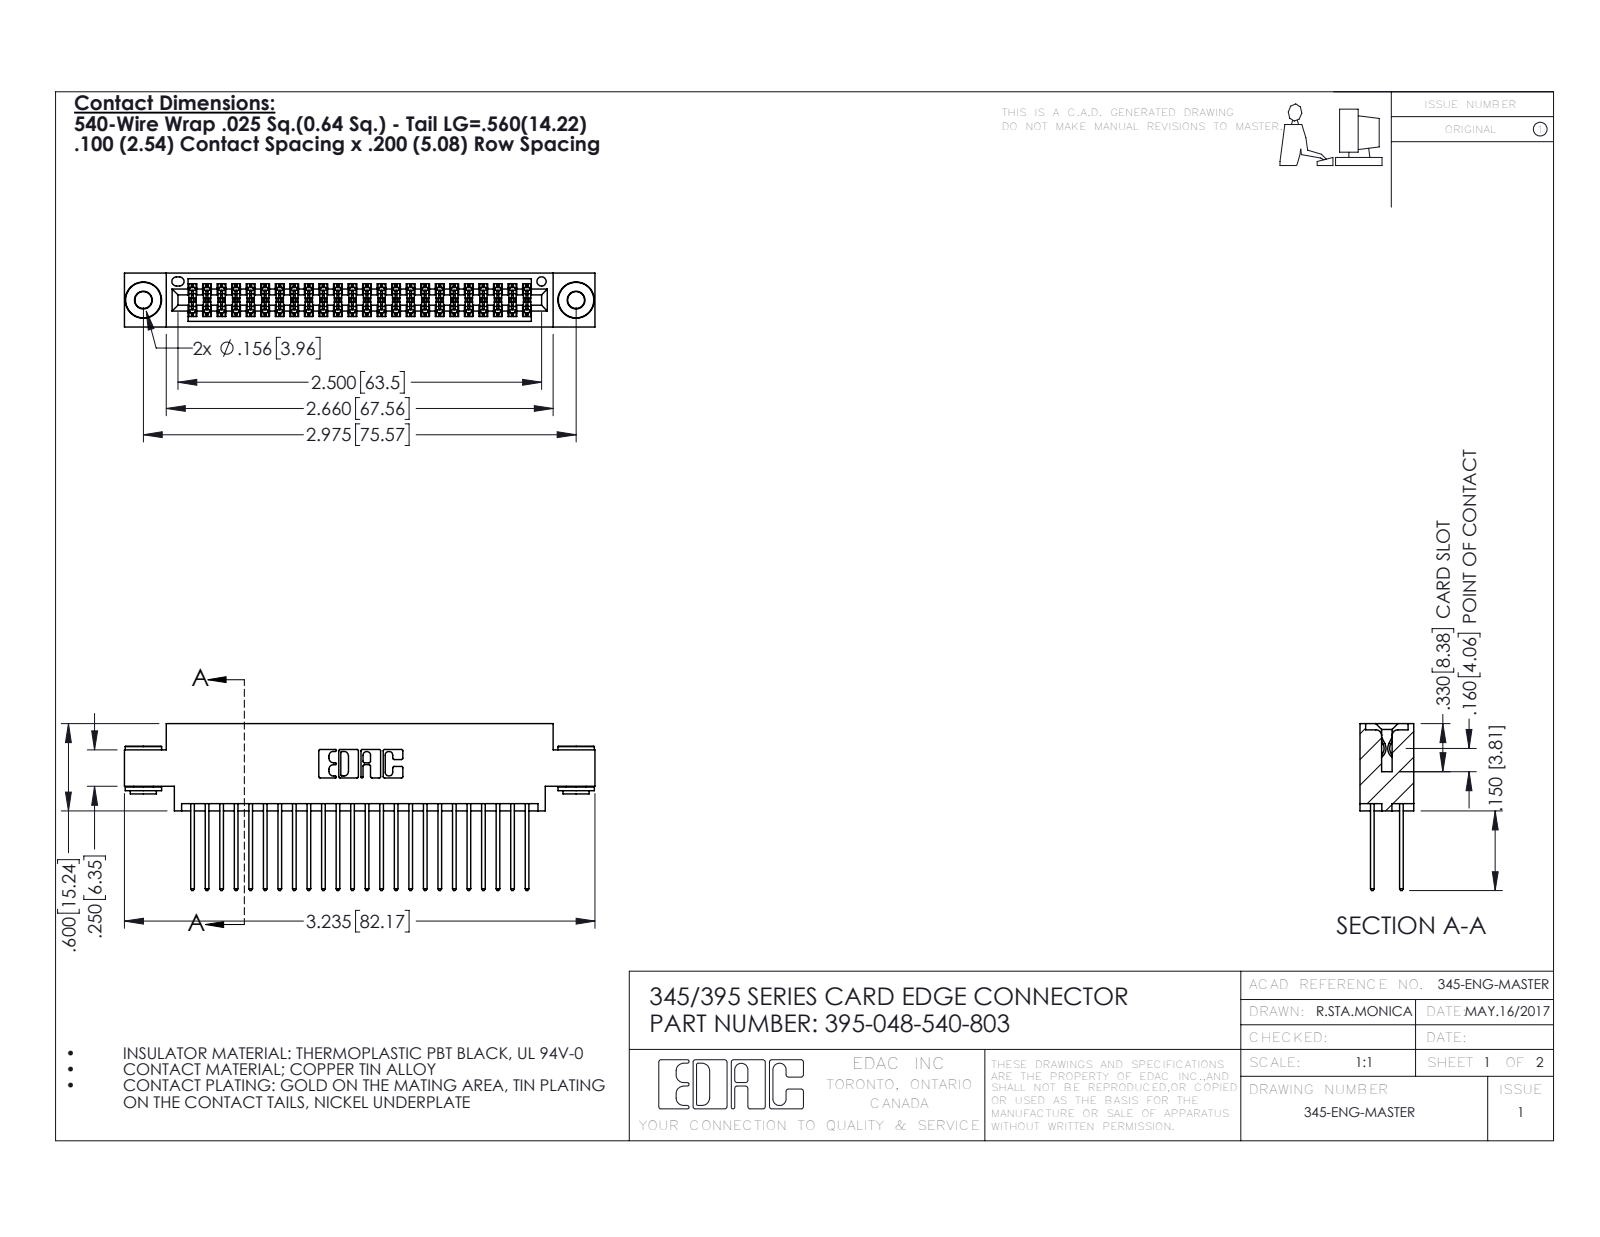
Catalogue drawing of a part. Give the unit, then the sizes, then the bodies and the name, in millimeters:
Units: millimetres
Overall size (bounding box): 82.2 × 29.1 × 9.4
Round holes (diameter × count): ⌀2.9 ×2, ⌀4 ×2, ⌀1.6 ×1
Round bosses / shafts (diameter × count): ⌀6.4 ×2, ⌀4.6 ×2, ⌀3.5 ×2
Partial cylindrical surfaces — rounded edges, fillets, slot ends (radius × count): R0.2 ×72, R0.3 ×48, R0.3 ×22, R0.2 ×6, R0.8 ×6, R0.7 ×3, R0.4 ×2, R0.5 ×2
Main face-to-face distances: 1.8, 7.6, 5.1, 2.5, 6.9, 0.6, 9.4, 5.7, 4.4, 3.8
Hole centre spacings: 6.9, 69.6, 75.6
Volume: 7 900 mm³ · Surface area: 12 520 mm²
Bodies: 51 solids, 2568 faces (1678 planar, 882 cylindrical, 8 other)
Part name (STEP PRODUCT): 345 Part_0.170 Offset - 0.156 Dia-TH; 345-292-001_345-293-140; 395-048-540-803; 345-250-002_345-250-002-102
STEP written by: SolidWorks 2016 (CONFIG_CONTROL_DESIGN)
